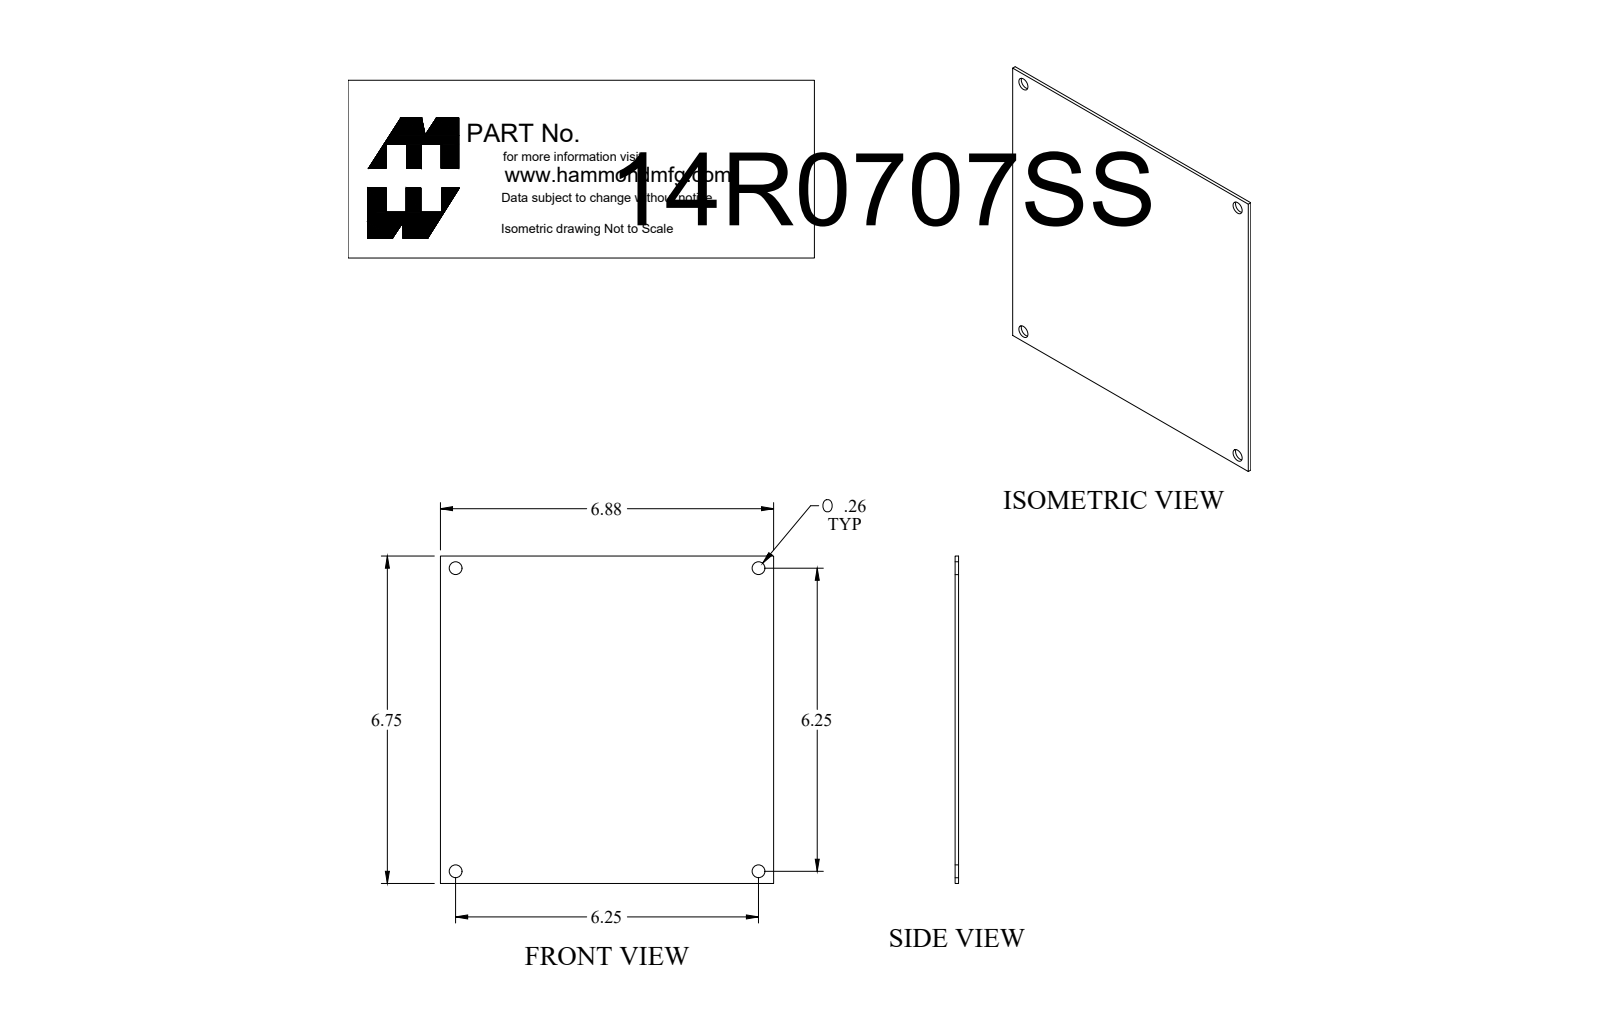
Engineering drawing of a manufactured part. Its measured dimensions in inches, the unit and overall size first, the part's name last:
Units: inches
Overall size (bounding box): 6.875 × 6.75 × 0.072
Round holes (diameter × count): ⌀0.265 ×4
Main face-to-face distances: 0.072, 6.75, 6.875
Hole centre spacings: 6.25, 6.25, 8.839
Volume: 3.325 in³ · Surface area: 94.57 in²
Bodies: 1 solid, 10 faces (6 planar, 4 cylindrical, 0 other)
Part name (STEP PRODUCT): 14R0707SS
STEP written by: SolidWorks 2018 (AUTOMOTIVE_DESIGN)
